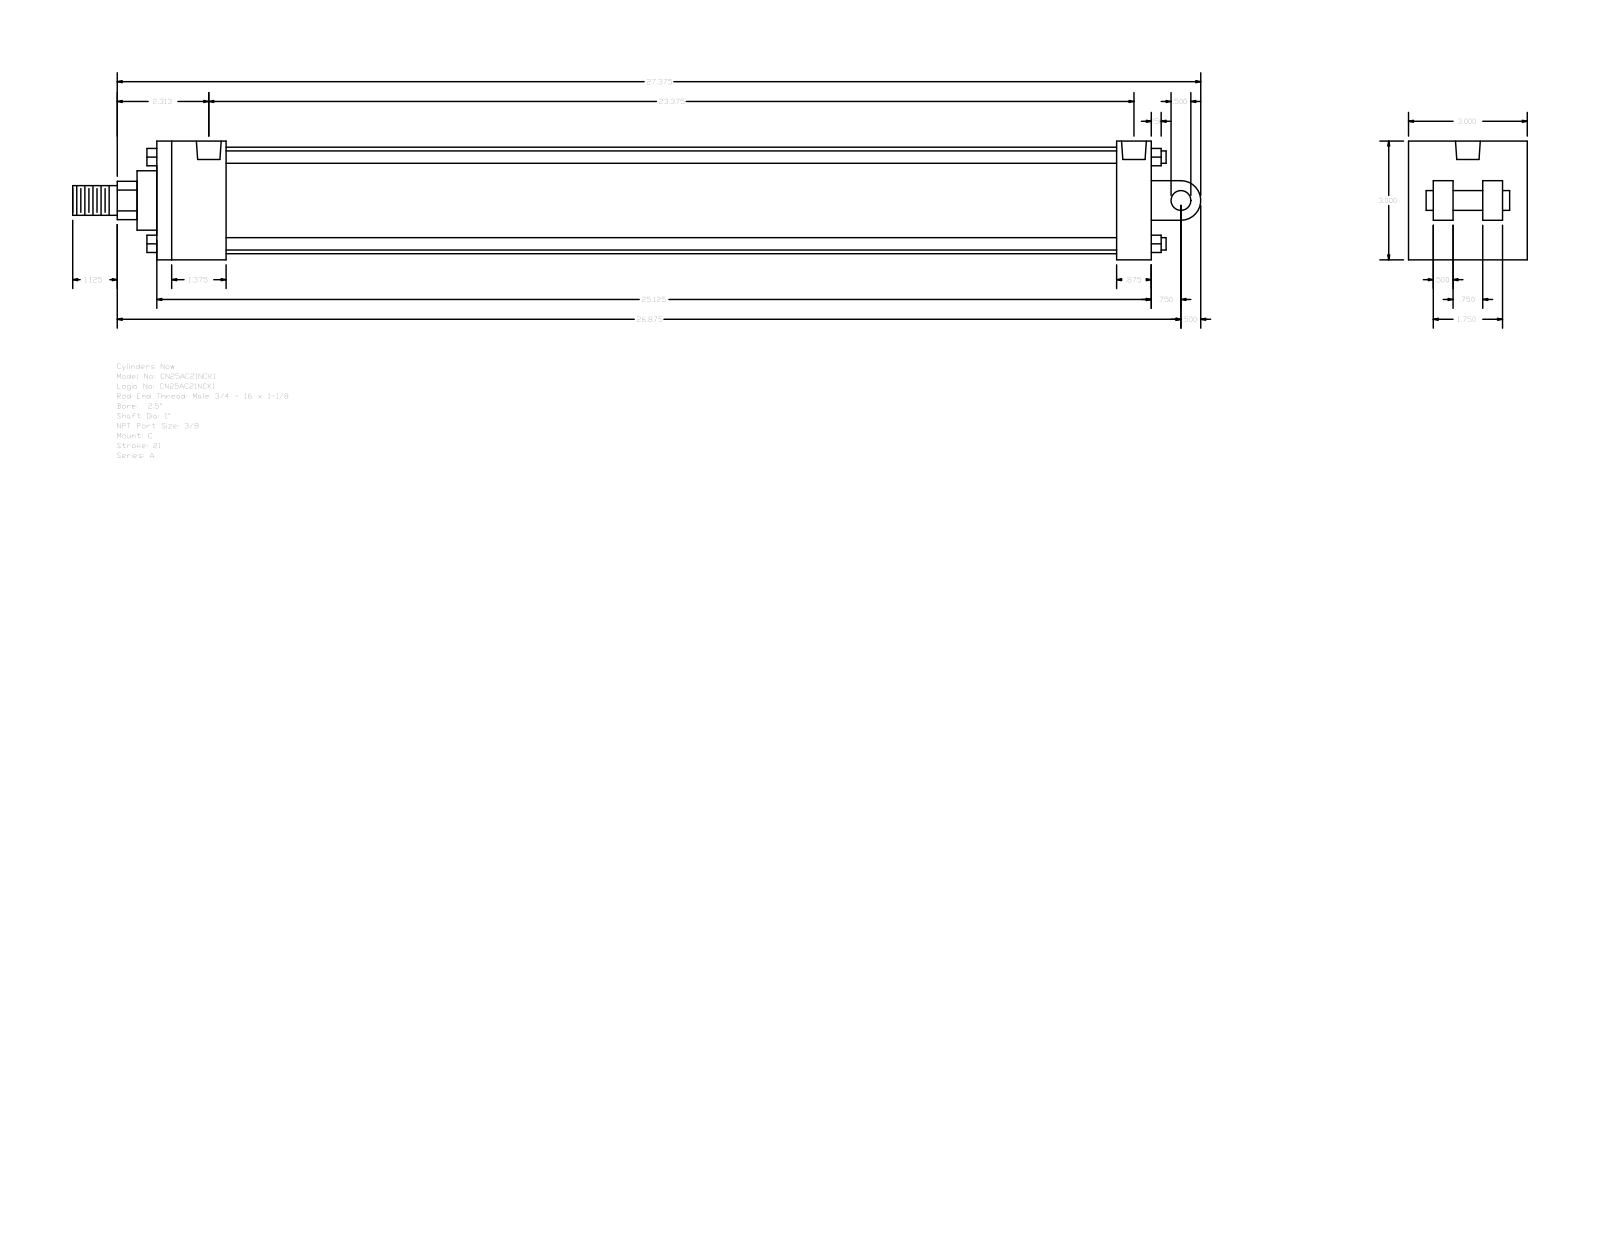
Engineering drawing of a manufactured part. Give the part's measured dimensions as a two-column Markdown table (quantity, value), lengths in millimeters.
| quantity | value |
| --- | --- |
| part name | A_C__0250_1 |
| STEP written by | GSSL Pune (CONFIG_CONTROL_DESIGN) |
| units | millimeters |
| bodies | 0 solids, 135 faces (102 planar, 33 cylindrical, 0 other) |
| overall size | 723.9 × 76.2 × 76.2 |
| round holes (diameter × count) | 5.56 × 4, 15.93 × 2 |
| round bosses / shafts (diameter × count) | 7.94 × 4, 68.33 × 1, 38.1 × 1, 25.4 × 1, 19.05 × 1, 12.7 × 1 |
| partial cylindrical surfaces (radius × count) | 12.29 × 1, 12.7 × 1 |
| main face-to-face distances | 76.2, 638.18, 12.7, 44.45, 615.95, 571.5, 593.73, 22.23, 15.87, 25.4 |
| hole center spacings | 2.38, 596.1, 598.48, 593.72 |
